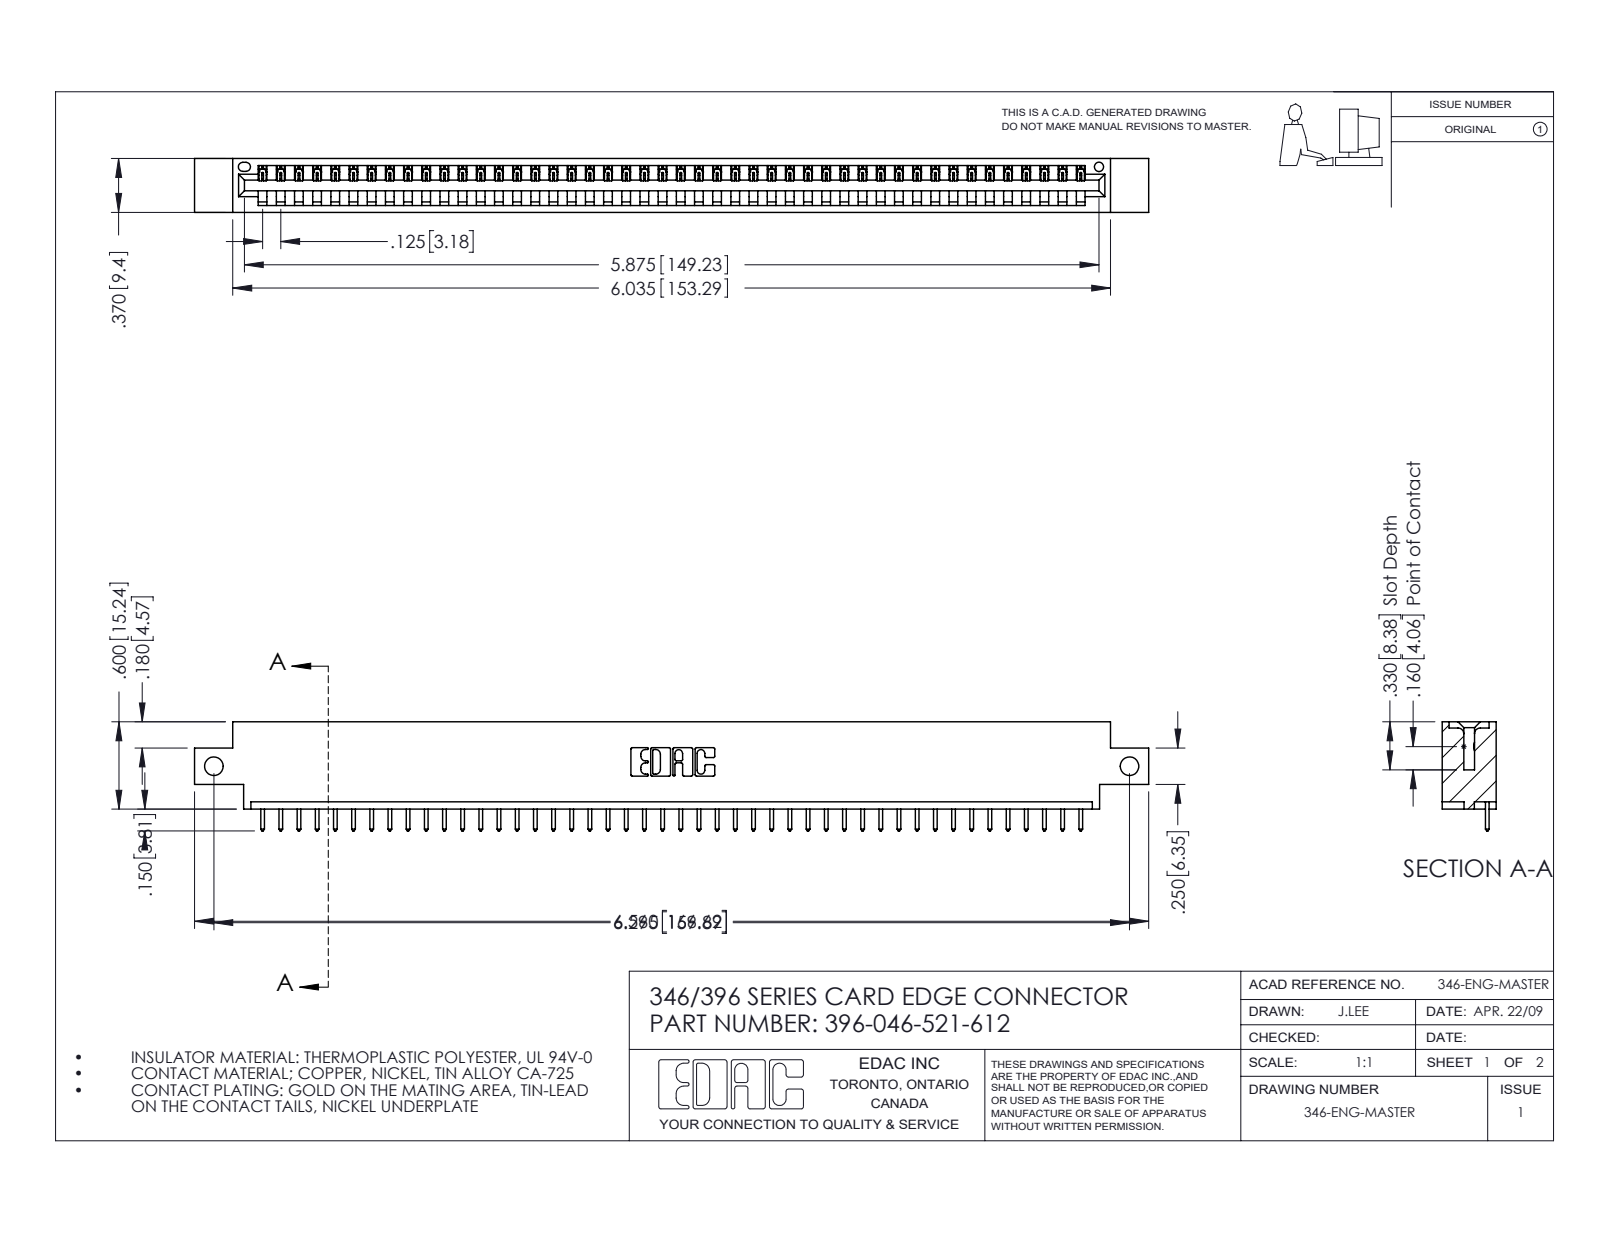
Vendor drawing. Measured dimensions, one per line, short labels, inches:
name: 396-046-521-612; 345-292-001_345-293-121; 346 Part_0.170 Offset - Side Mount
written by: SolidWorks 2016 (CONFIG_CONTROL_DESIGN)
unit: in
bodies: 47 solids, 2794 faces (1920 planar, 874 cylindrical, 0 other)
size: 6.56 × 0.75 × 0.37
volume: 0.952 in³; area: 29.51 in²
holes: 2× ⌀0.128, 1× ⌀0.064
rounds: 92× R0.006, 92× R0.01, 22× R0.01, 6× R0.007, 6× R0.031, 3× R0.026, 2× R0.031, 2× R0.04
face distances: 0.048, 0.322, 0.37, 0.25, 0.072, 0.298, 0.025, 0.148, 0.222, 0.1
hole spacings: 6.295
